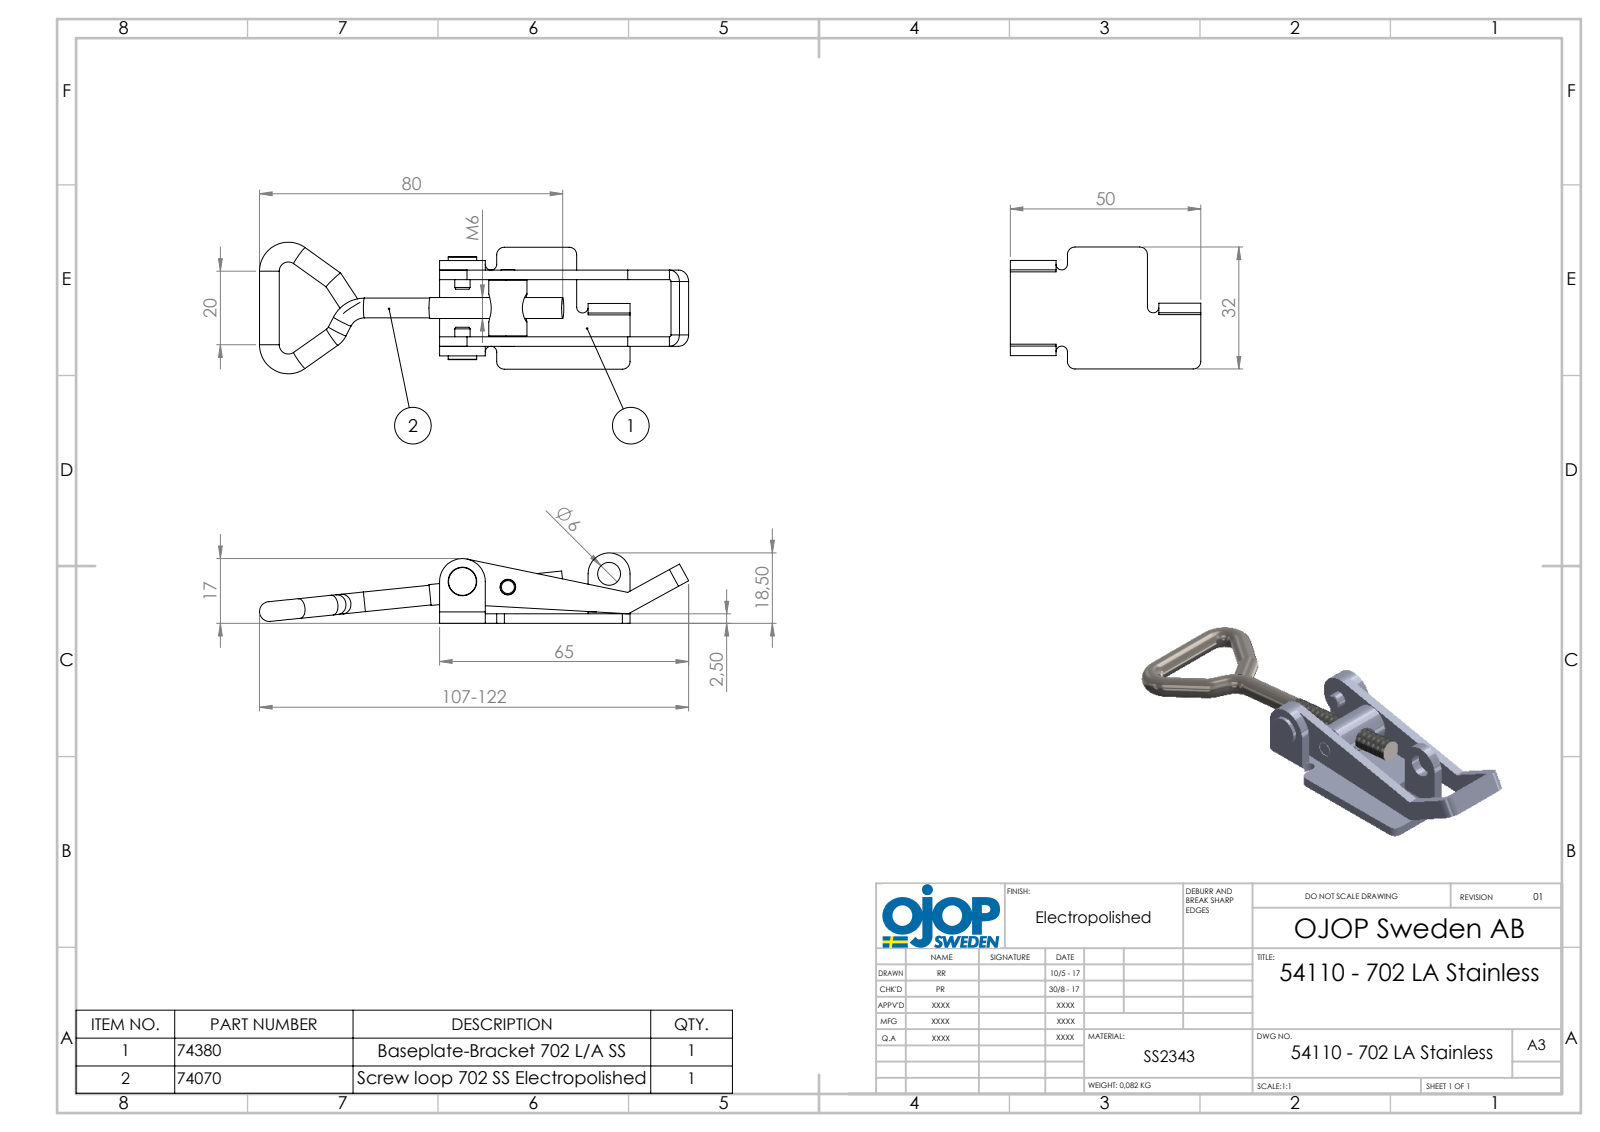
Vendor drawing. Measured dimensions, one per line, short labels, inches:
name: 702 - Skruvögla; 702 - Rulle; 54110 - 702 LA Stainless; 702 - Bygel (+2 more)
written by: SolidWorks 2015 (AUTOMOTIVE_DESIGN)
unit: in
bodies: 6 solids, 163 faces (65 planar, 72 cylindrical, 26 other)
size: 4.35 × 1.359 × 0.728
volume: 0.677 in³; area: 16.4 in²
holes: 2× ⌀0.161, 2× ⌀0.236, 1× ⌀0.197
bosses: 6× ⌀0.204, 2× ⌀0.157, 1× ⌀0.394, 1× ⌀0.295, 1× ⌀0.217
rounds: 5× R0.02, 5× R0.118, 4× R0.079, 2× R0.059, 1× R0.059, 1× R0.217, 1× R0.236
face distances: 0.098, 0.689, 0.787, 0.344, 0.443, 0.591, 0.197, 0.246, 0.886, 0.236
hole spacings: 0.473, 1.055, 1.518
